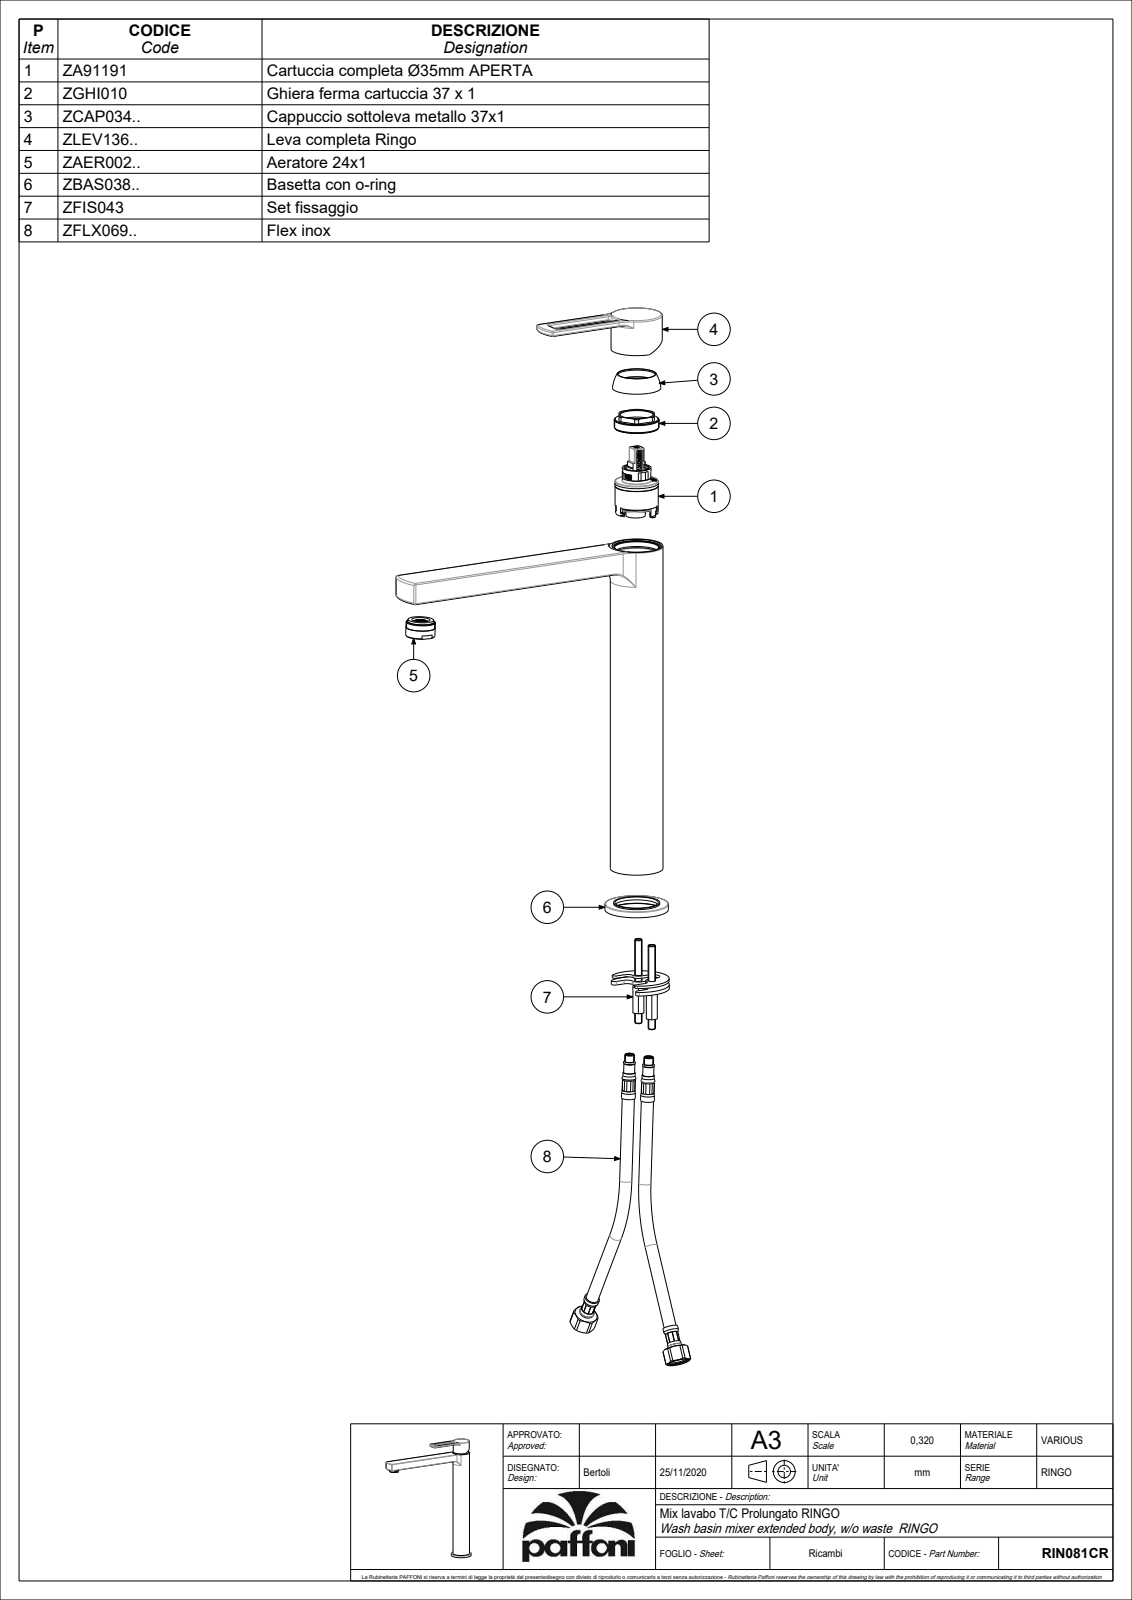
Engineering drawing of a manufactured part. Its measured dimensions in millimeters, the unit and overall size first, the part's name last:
Units: millimetres
Overall size (bounding box): 310.42 × 248 × 52
Round holes (diameter × count): ⌀5.5 ×2, ⌀8 ×2, ⌀3 ×1, ⌀3.4 ×1, ⌀3.5 ×1, ⌀4 ×1, ⌀4.6 ×1, ⌀7.8 ×1, ⌀16 ×1, ⌀17 ×1, ⌀19.5 ×1, ⌀19.7 ×1
Round bosses / shafts (diameter × count): ⌀9.3 ×2, ⌀4.8 ×2, ⌀52 ×1, ⌀43.2 ×1, ⌀42.6 ×1, ⌀42 ×1, ⌀37.8 ×1, ⌀35.4 ×1
Partial cylindrical surfaces — rounded edges, fillets, slot ends (radius × count): R0.5 ×54, R1 ×30, R1.5 ×20, R3 ×18, R2 ×9, R0.2 ×6, R1.7 ×6, R0.8 ×4
Main face-to-face distances: 3.5, 14.5, 18, 11, 27.5, 31, 1, 24, 7.5, 45.05
Hole centre spacings: 13.6, 8.6, 22.2, 9.71, 14, 14.64, 15.81, 19.52
Volume: 230 715 mm³ · Surface area: 143 957 mm²
Bodies: 2 solids, 3358 faces (2397 planar, 517 cylindrical, 444 other)
Part name (STEP PRODUCT): RIN081CR
STEP written by: CREO PARAMETRIC BY PTC INC, 2020044 (CONFIG_CONTROL_DESIGN)
